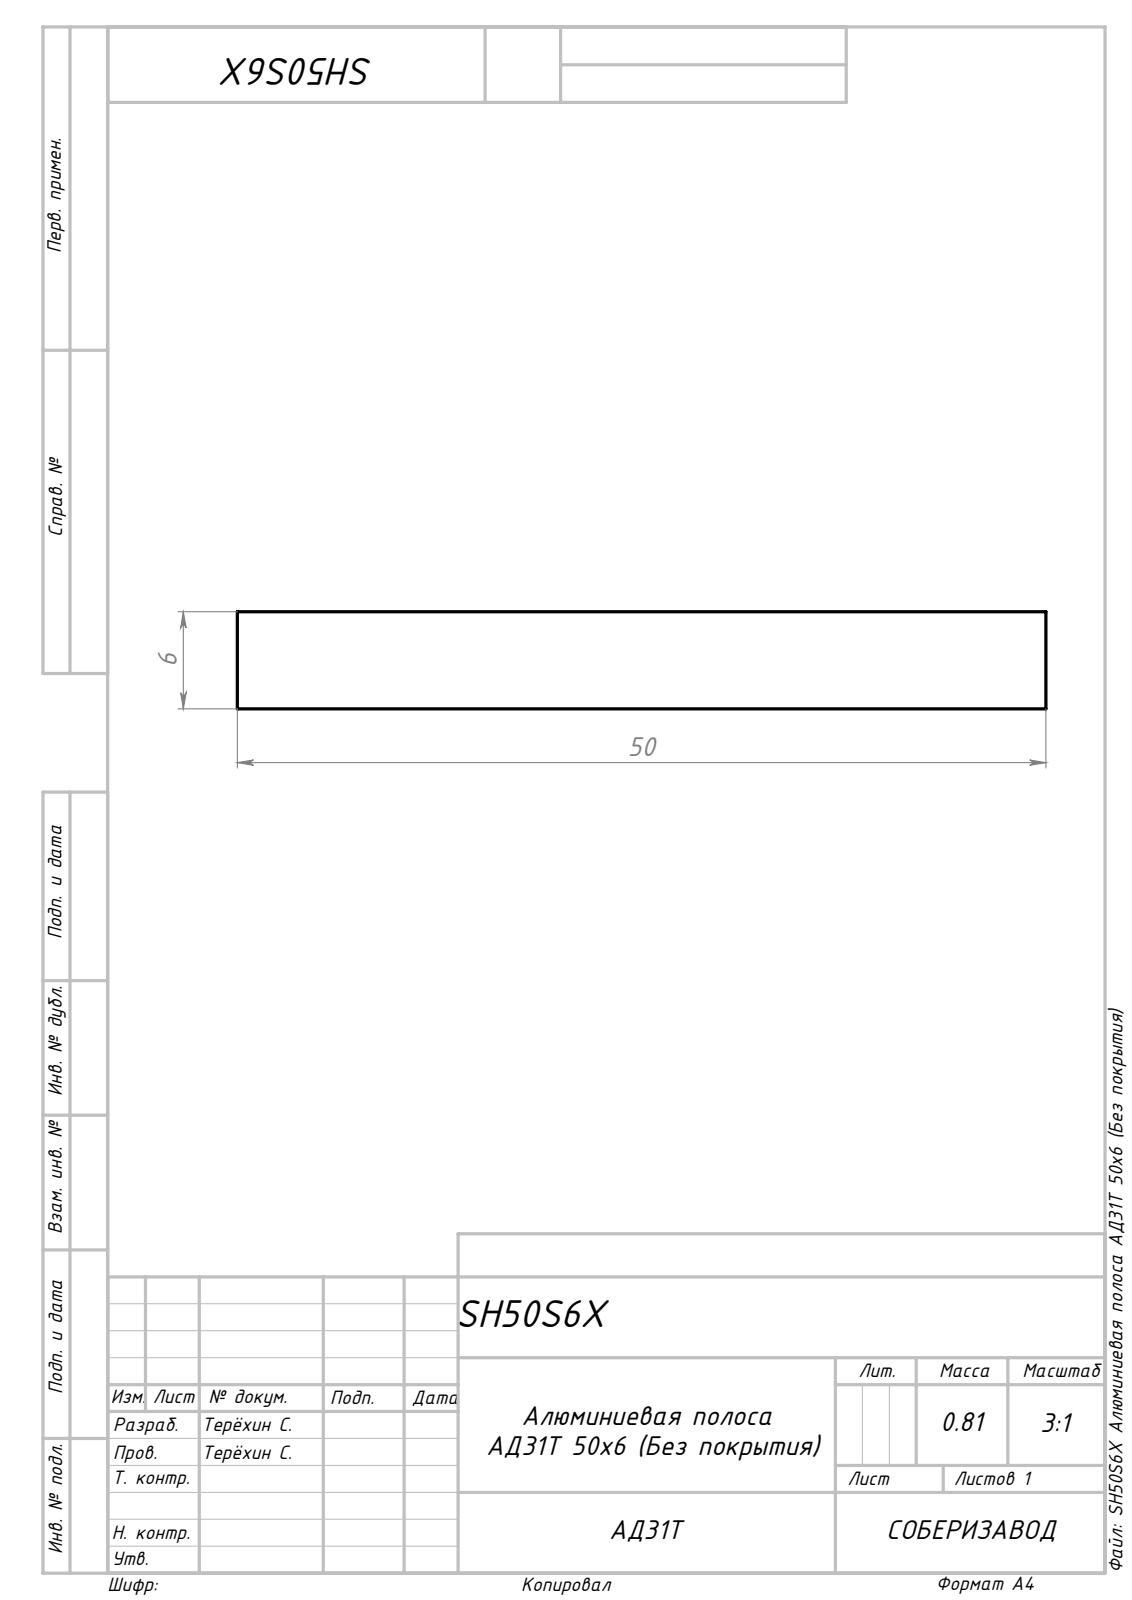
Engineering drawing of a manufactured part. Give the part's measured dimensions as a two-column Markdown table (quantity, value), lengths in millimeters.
| quantity | value |
| --- | --- |
| part name | Сборка1; SH50S6X Алюминиевая полоса АД31Т 50х6 (Без покрытия)_50х6 |
| STEP written by | SolidWorks 2024 (AUTOMOTIVE_DESIGN) |
| units | millimeters |
| bodies | 1 solid, 6 faces (6 planar, 0 cylindrical, 0 other) |
| overall size | 1000 × 50 × 6 |
| volume | 300 000 mm³ |
| surface area | 112 600 mm² |
| main face-to-face distances | 6, 50, 1000 |
